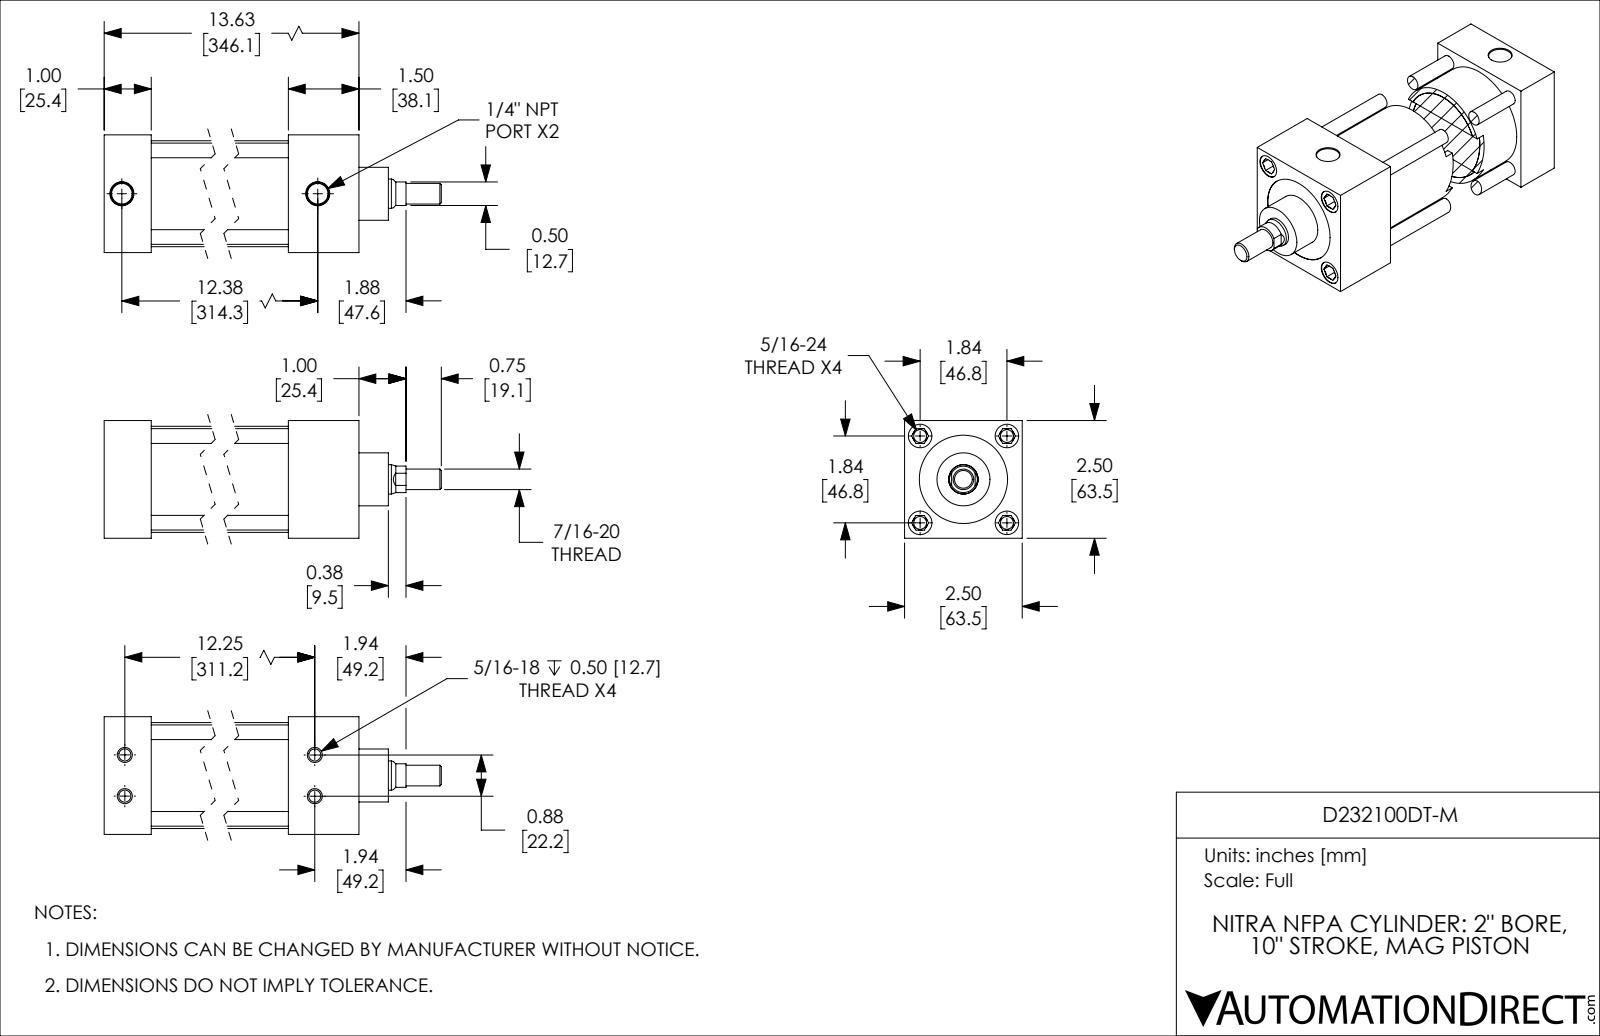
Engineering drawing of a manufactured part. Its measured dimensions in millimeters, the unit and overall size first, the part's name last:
Units: millimetres
Overall size (bounding box): 390.5 × 63.5 × 63.5
Round holes (diameter × count): ⌀6.9 ×7, ⌀6.5 ×4, ⌀12.7 ×4, ⌀11.1 ×2, ⌀15.9 ×1, ⌀47.6 ×1, ⌀50.8 ×1
Round bosses / shafts (diameter × count): ⌀7.9 ×4, ⌀57.2 ×1, ⌀50.8 ×1, ⌀28.6 ×1, ⌀15.8 ×1, ⌀11.1 ×1
Partial cylindrical surfaces — rounded edges, fillets, slot ends (radius × count): R7.1 ×1
Main face-to-face distances: 63.5, 25.4, 308, 282.6, 28.6, 54, 254, 38.1, 346.1, 320.7
Hole centre spacings: 46.7, 46.8, 33, 11.2, 11.3, 22.2, 33.1, 66.1
Volume: 572 200 mm³ · Surface area: 189 900 mm²
Bodies: 2 solids, 200 faces (58 planar, 62 cylindrical, 80 other)
Part name (STEP PRODUCT): D232100DT-M; D232100DT-M_PISTON_KK1; D232100DT-M_BODY
STEP written by: SolidWorks 2019 (CONFIG_CONTROL_DESIGN)
